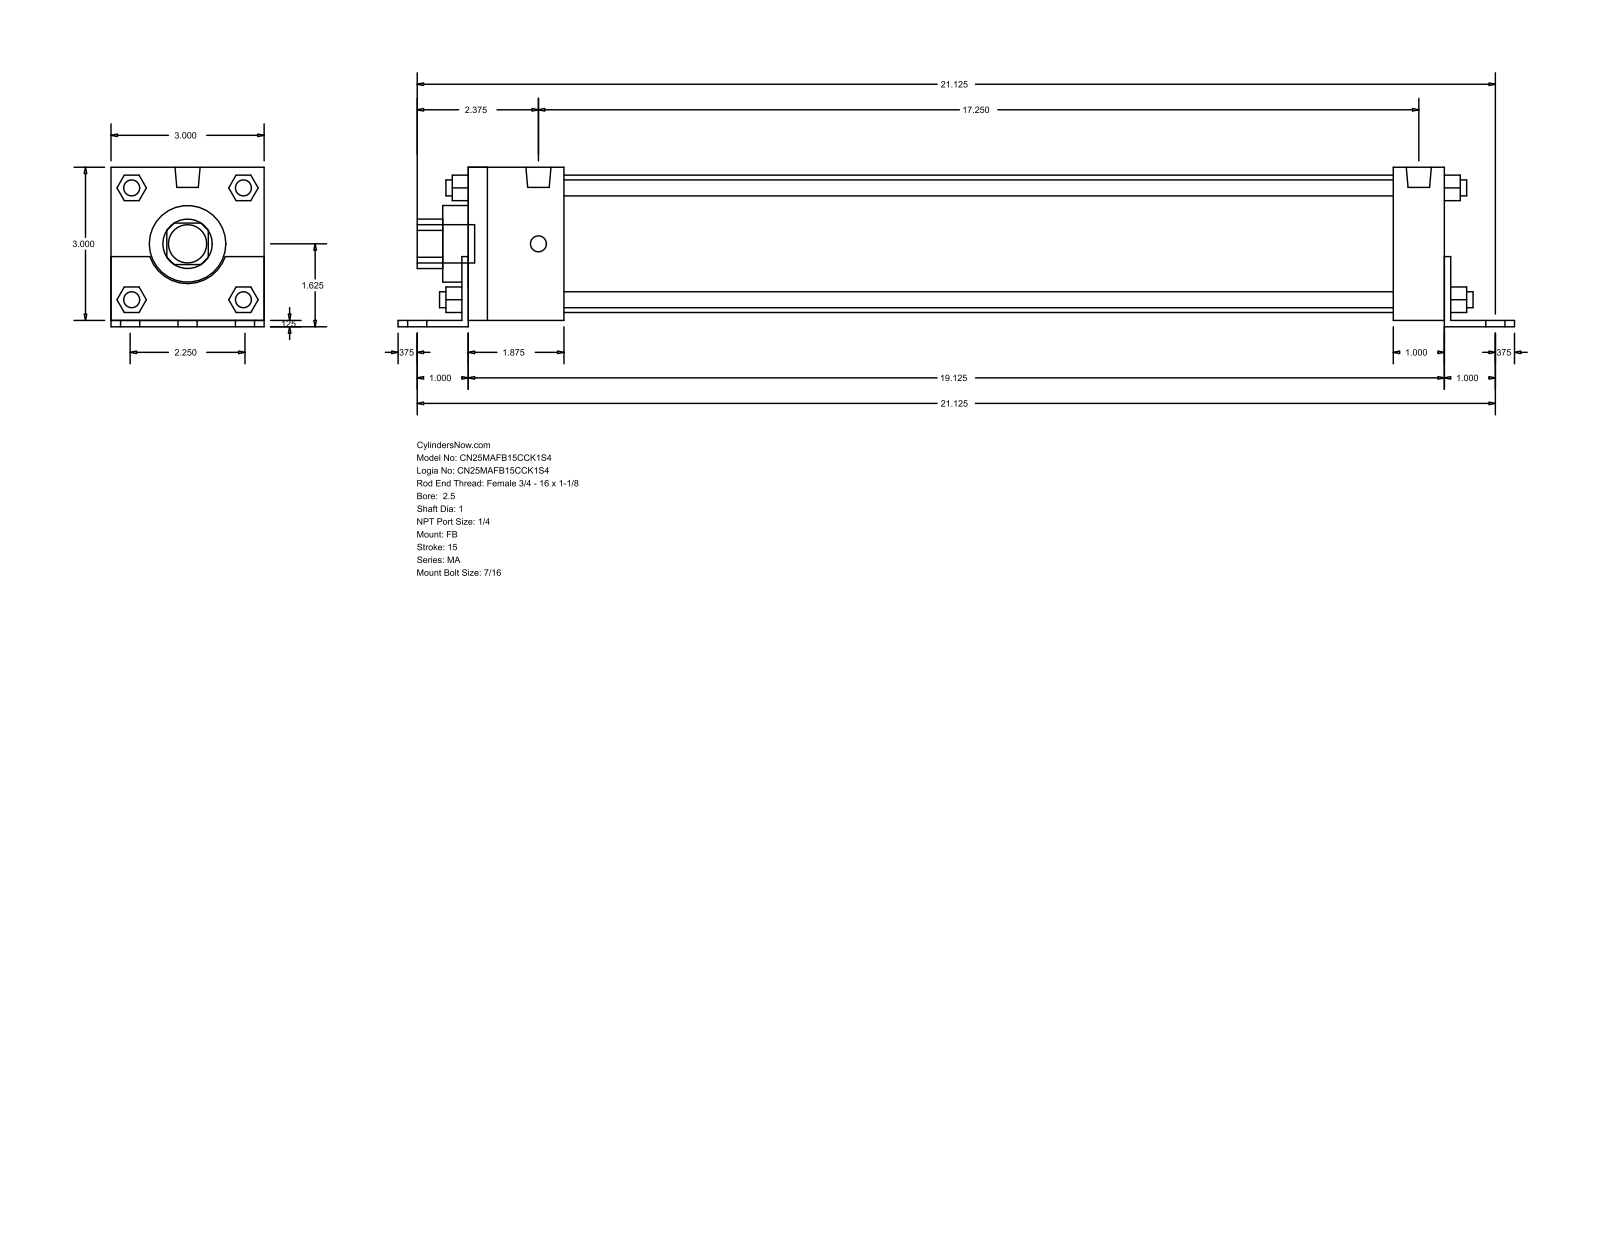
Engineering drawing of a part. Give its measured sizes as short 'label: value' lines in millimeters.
name: MA_FB__0250_1
written by: GSSL Pune (CONFIG_CONTROL_DESIGN)
unit: mm
bodies: 0 solids, 140 faces (105 planar, 35 cylindrical, 0 other)
size: 555.62 × 79.38 × 76.2
holes: 1× ⌀25.4, 1× ⌀38.1, 1× ⌀68.33
bosses: 8× ⌀7.94, 6× ⌀11.11, 2× ⌀12.49, 1× ⌀19.05
rounds: 1× R12.29, 1× R19.81
face distances: 76.2, 3.17, 79.37, 488.95, 485.78, 12.7, 47.63, 438.15, 441.32, 460.37
